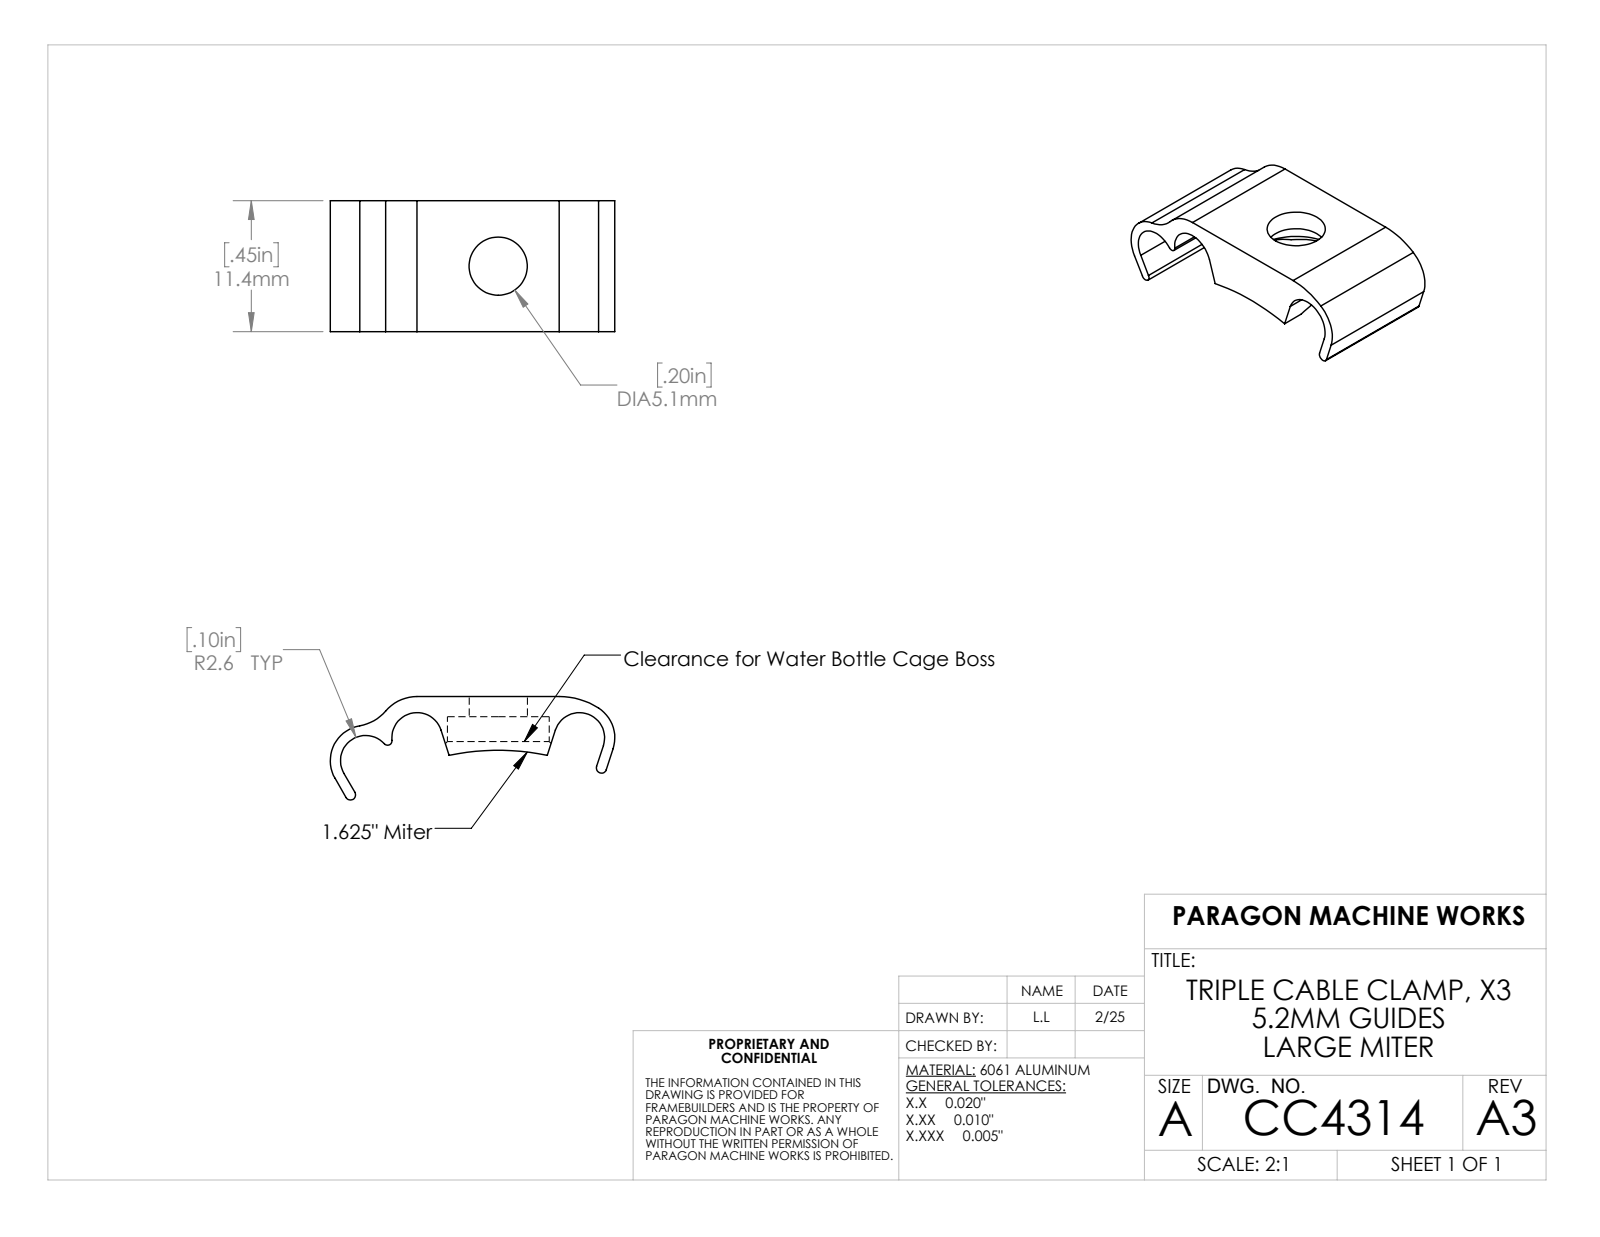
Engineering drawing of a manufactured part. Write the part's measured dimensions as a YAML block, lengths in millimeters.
part_name: "CC4314"
step_written_by: "SolidWorks 2023 (AUTOMOTIVE_DESIGN)"
units: millimeters
bodies: {solids: 1, faces: 32, planar: 10, cylindrical: 20, other: 2}
overall_size: [27.1, 11.4, 10]
volume: 660
surface_area: 1182
round_holes:
  - {diameter: 5.1, count: 1}
  - {diameter: 8.9, count: 1}
partial_cylinders:
  - {radius: 2.6, count: 3}
  - {radius: 3.5, count: 3}
  - {radius: 0.4, count: 1}
  - {radius: 0.4, count: 1}
  - {radius: 0.5, count: 1}
  - {radius: 3.8, count: 1}
  - {radius: 20.9, count: 1}
face_to_face_distances: [11.4, 0.9, 1.9, 5.2, 6.1]
